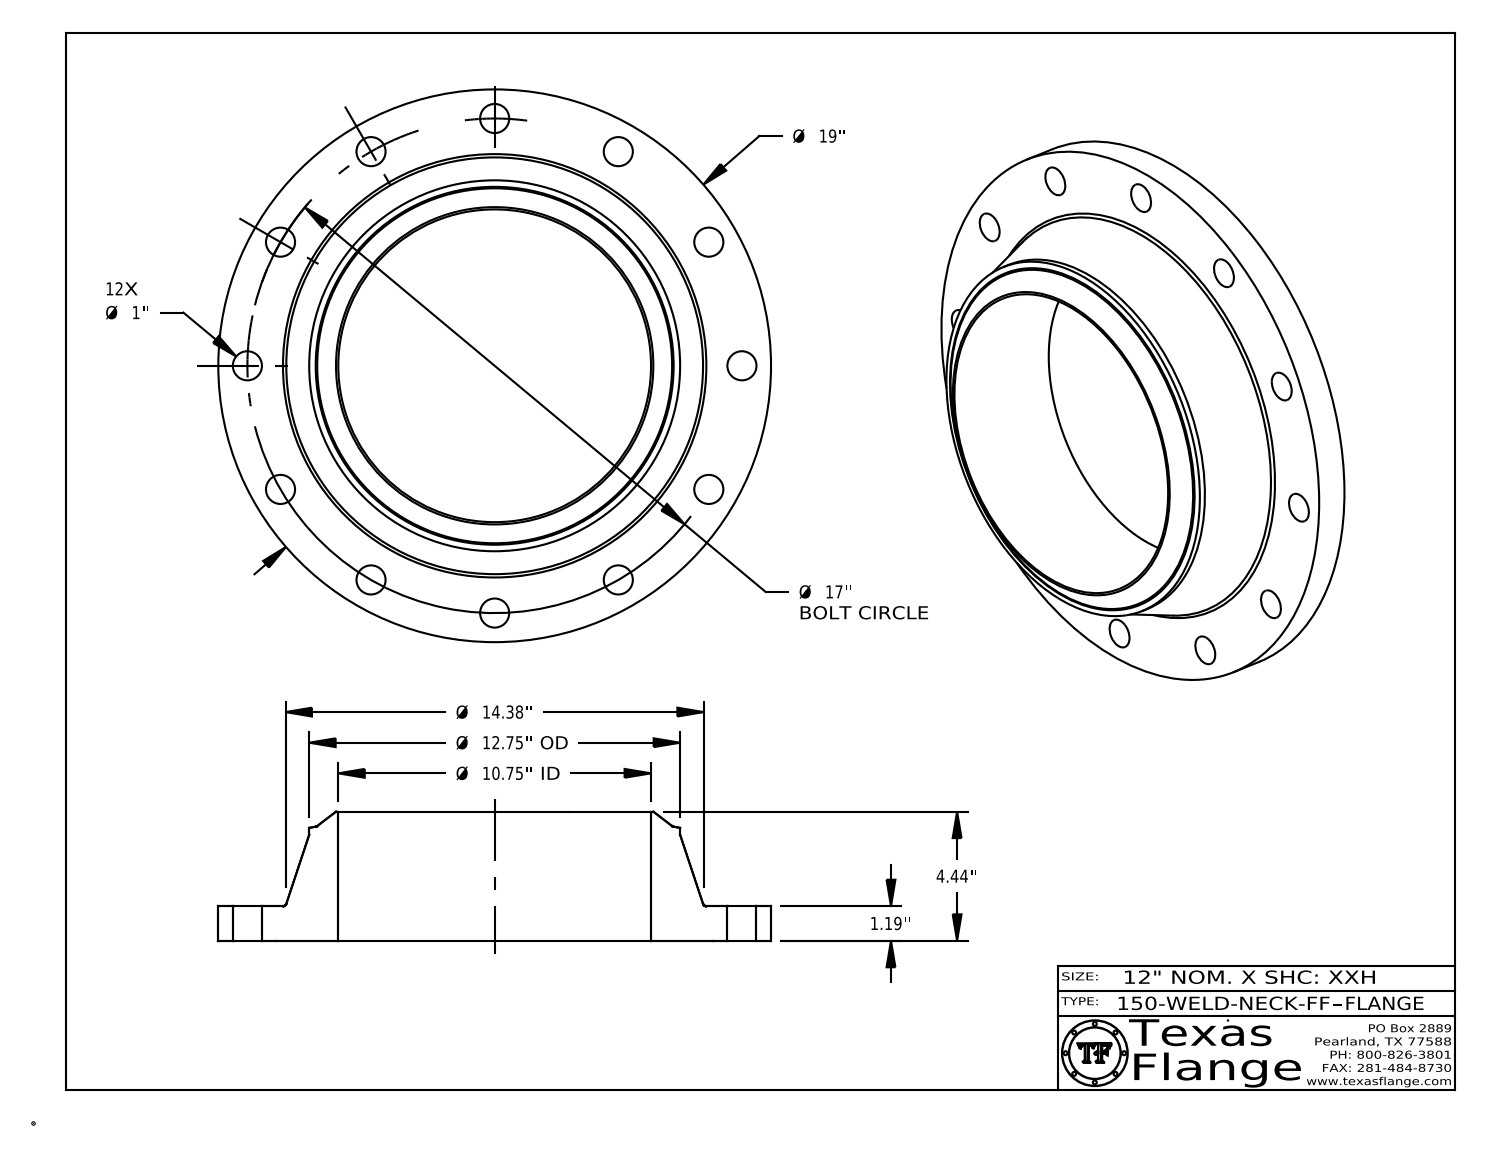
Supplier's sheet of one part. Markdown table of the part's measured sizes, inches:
| quantity | value |
| --- | --- |
| part name | 150-WELD-NECK-FF |
| STEP written by | CATIA V5 STEP AP214 (AUTOMOTIVE_DESIGN) |
| units | inches |
| bodies | 1 solid, 429 faces (369 planar, 50 cylindrical, 10 other) |
| overall size | 19 × 19 × 4.44 |
| volume | 368.3 in³ |
| surface area | 723 in² |
| round holes (diameter × count) | 1 × 12, 0.495 × 1, 10.75 × 1 |
| round bosses / shafts (diameter × count) | 0.03 × 8, 19 × 1, 12.75 × 1, 0.39 × 1 |
| main face-to-face distances | 1.19, 4.44, 3.25, 0.015, 1.175, 3.265, 0.148, 0.145, 0.027, 0.096 |
| hole center spacings | 8.5, 16.42, 4.4, 12.02, 14.722, 4.4, 12.021, 14.722 |
